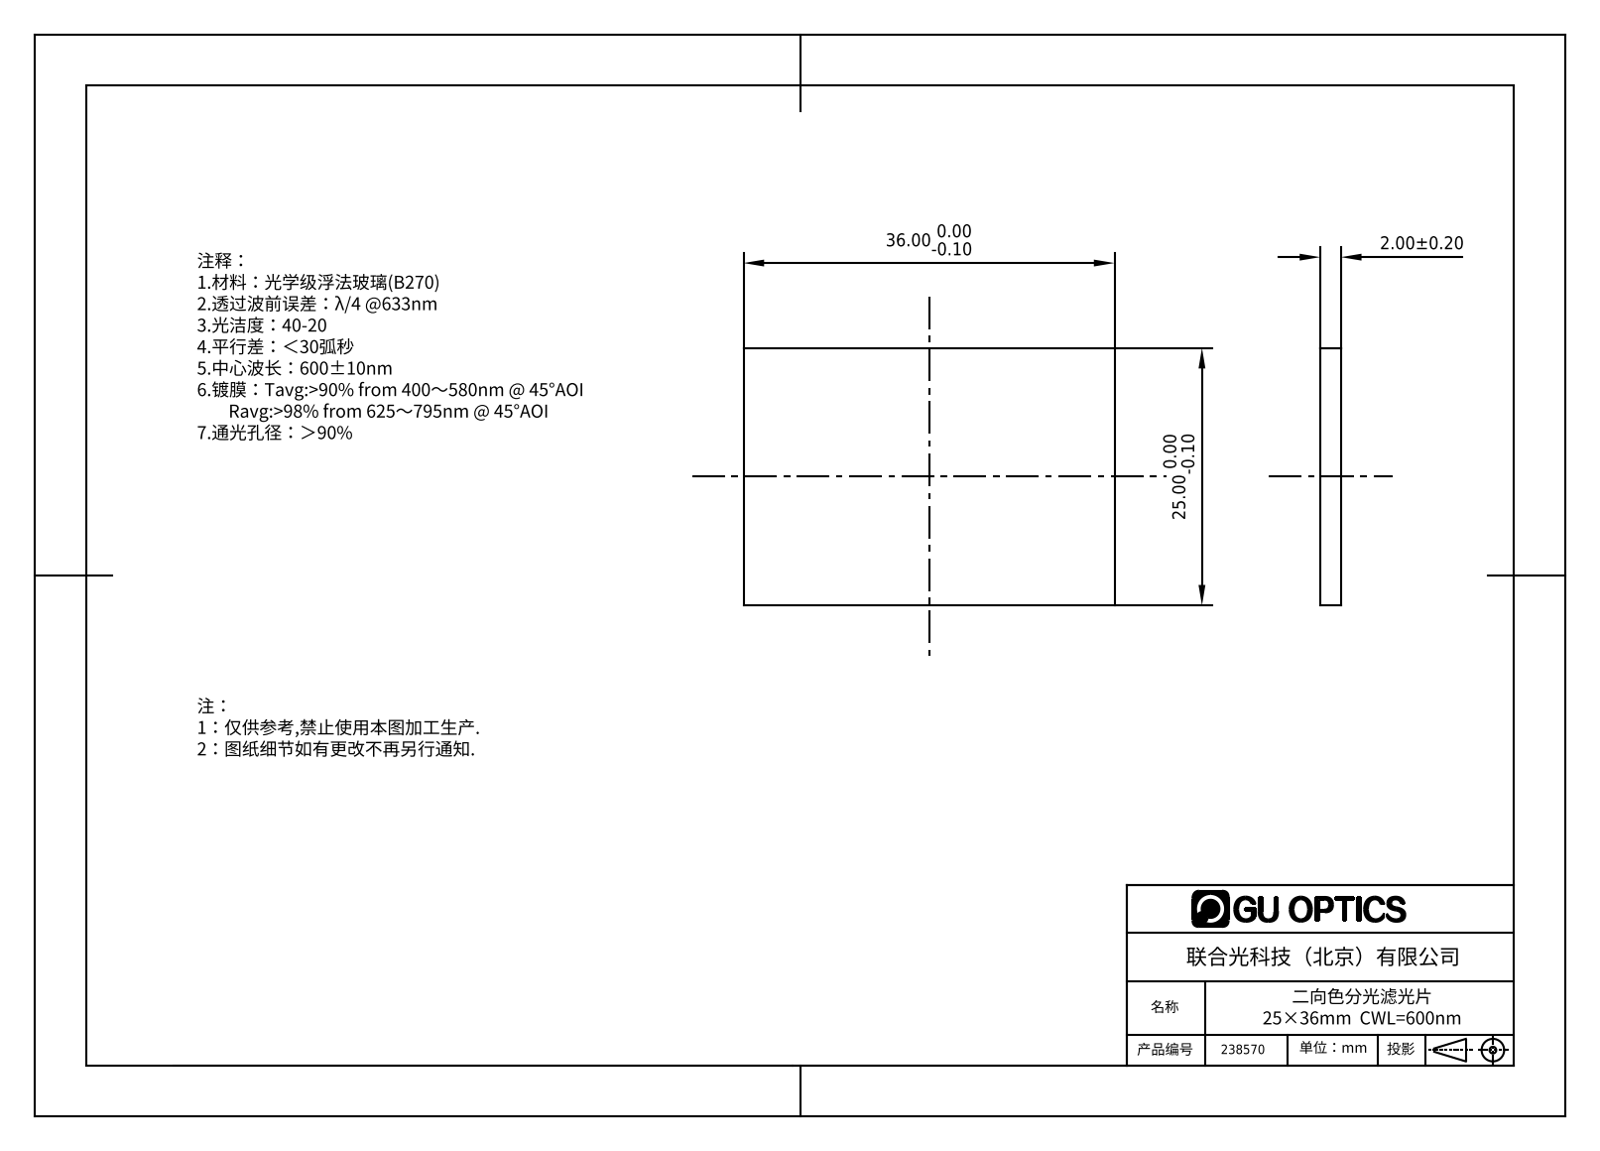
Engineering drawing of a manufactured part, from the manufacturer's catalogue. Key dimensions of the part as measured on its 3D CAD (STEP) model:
Part name (STEP PRODUCT): 238567
STEP written by: SolidWorks 2016 (AUTOMOTIVE_DESIGN)
Units: millimetres
Bodies: 1 solid, 6 faces (6 planar, 0 cylindrical, 0 other)
Overall size (bounding box): 36 × 25 × 2
Volume: 1 800 mm³ · Surface area: 2 044 mm²
Main face-to-face distances: 2, 25, 36
